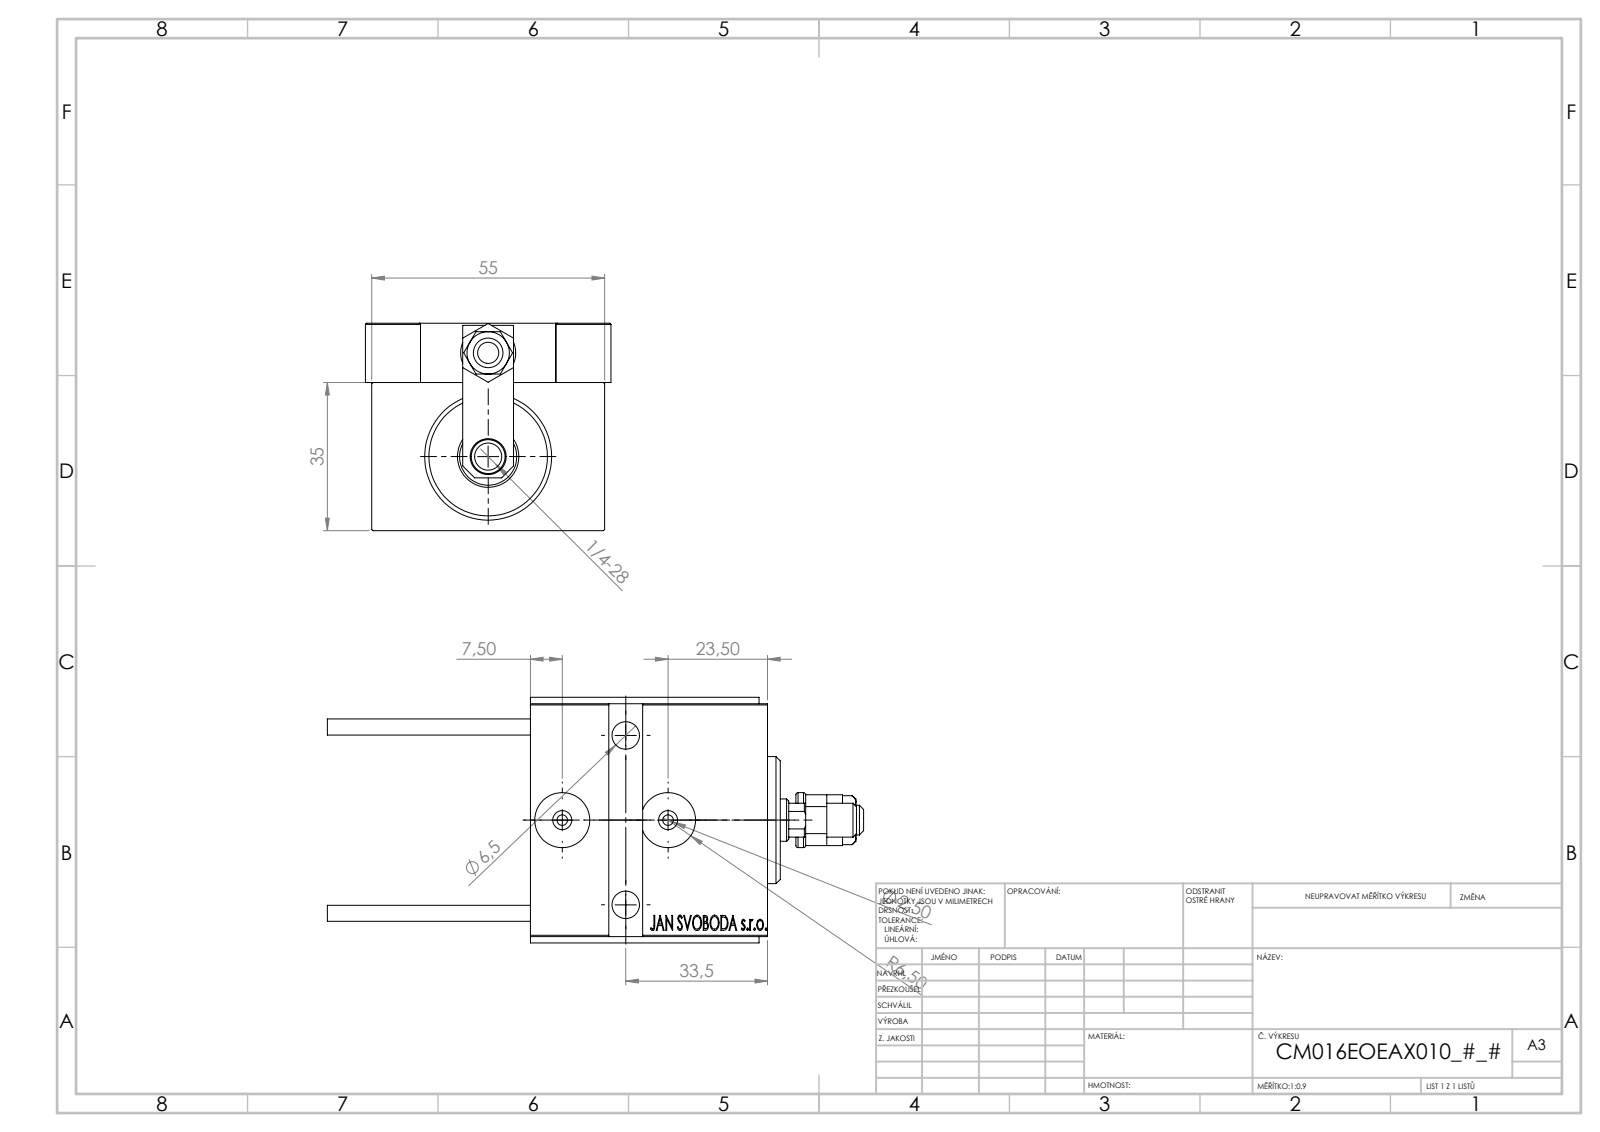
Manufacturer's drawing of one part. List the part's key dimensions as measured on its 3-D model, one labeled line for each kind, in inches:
Part name (STEP PRODUCT): SWITCH X; NUT_D12; ALLEN BOLT D5; MAGNET (+8 more)
STEP written by: SolidWorks 2019 (CONFIG_CONTROL_DESIGN)
Units: inches
Bodies: 25 solids, 1303 faces (575 planar, 181 cylindrical, 547 other)
Overall size (bounding box): 4.988 × 2.283 × 1.929
Volume: 9.023 in³ · Surface area: 72.26 in²
Round holes (diameter × count): ⌀0.315 ×5, ⌀0.126 ×4, ⌀0.157 ×4, ⌀0.098 ×2, ⌀0.197 ×2, ⌀0.256 ×2, ⌀0.413 ×2, ⌀0.512 ×2, ⌀0.177 ×1, ⌀0.276 ×1, ⌀0.335 ×1, ⌀0.394 ×1
Round bosses / shafts (diameter × count): ⌀0.197 ×2, ⌀0.177 ×2, ⌀0.15 ×2, ⌀1.181 ×1, ⌀0.709 ×1, ⌀0.512 ×1, ⌀0.433 ×1, ⌀0.315 ×1
Partial cylindrical surfaces — rounded edges, fillets, slot ends (radius × count): R0.012 ×26, R0.118 ×2, R0.177 ×1
Main face-to-face distances: 0.551, 1.929, 1.378, 2.165, 0.197, 0.394, 0.059, 0.118, 1.732, 0.276
Hole centre spacings: 0.794, 0.984, 0.325, 0.406, 0.448, 0.759, 0.787, 0.88
